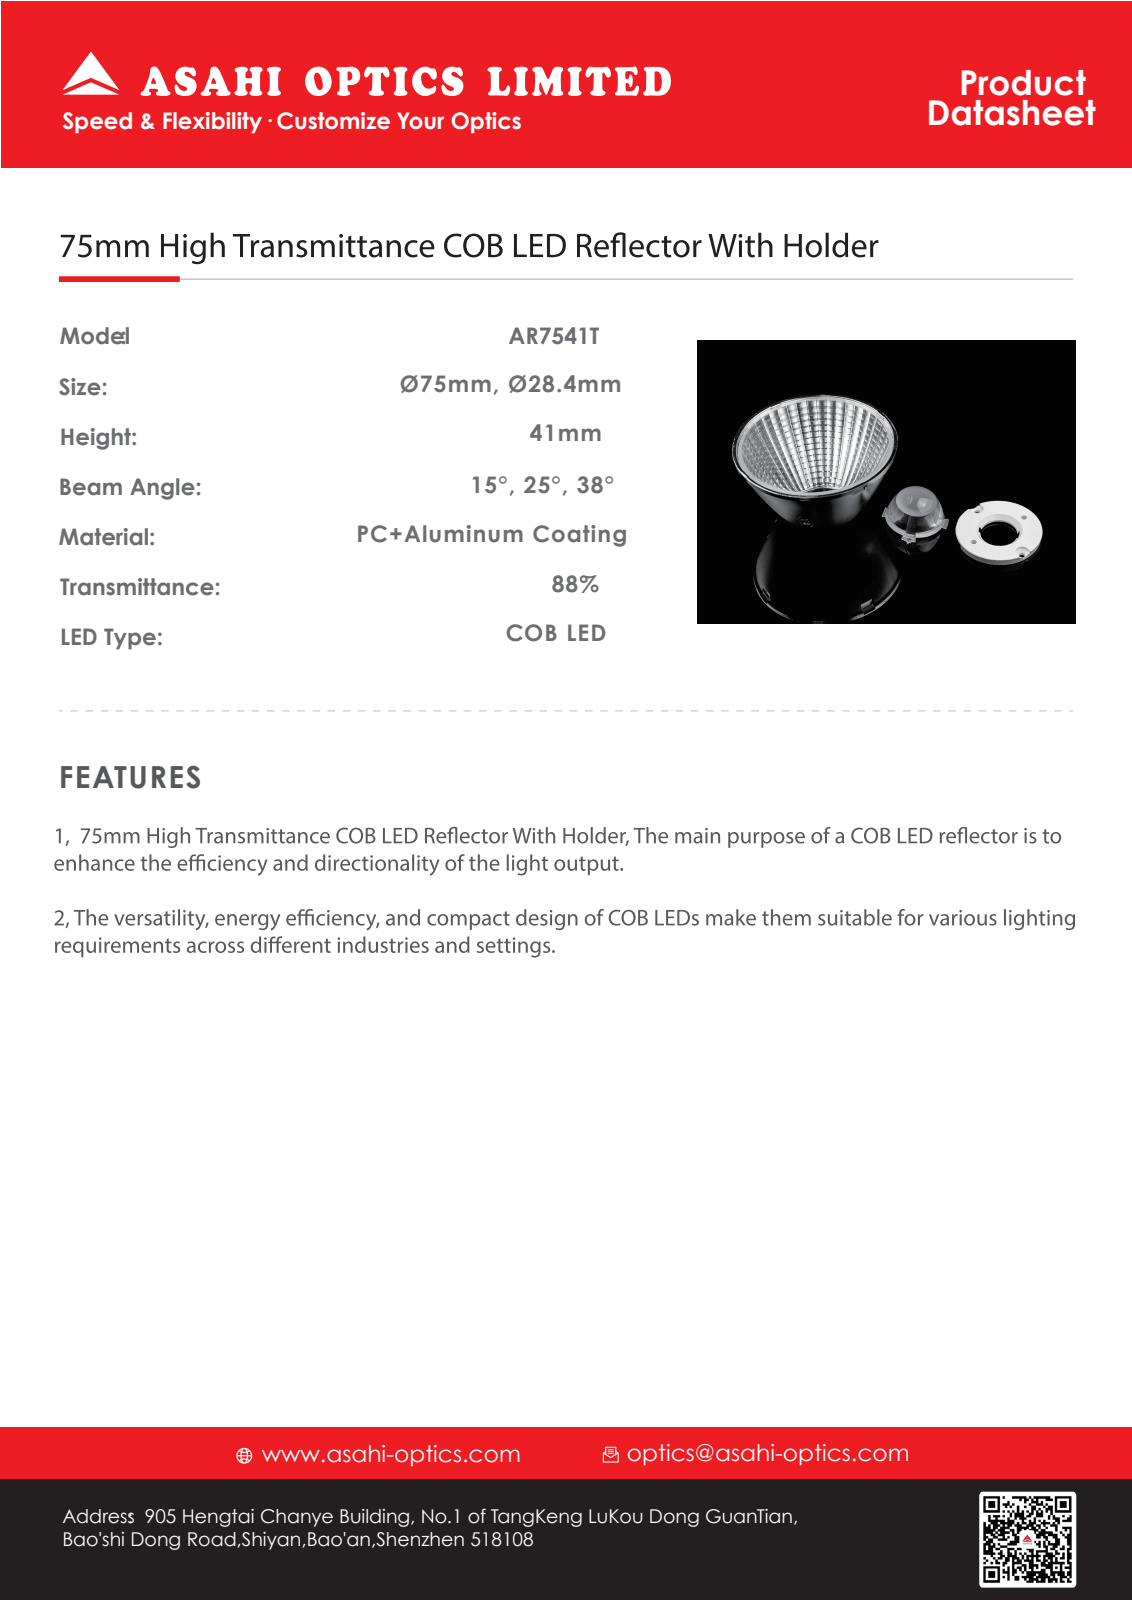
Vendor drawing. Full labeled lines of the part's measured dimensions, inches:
STEP written by: SolidWorks 2014 (CONFIG_CONTROL_DESIGN)
Units: inches
Bodies: 2 solids, 359 faces (233 planar, 73 cylindrical, 53 other)
Overall size (bounding box): 2.953 × 2.953 × 1.707
Volume: 0.728 in³ · Surface area: 30.04 in²
Round holes (diameter × count): ⌀1.118 ×1, ⌀2.831 ×1
Round bosses / shafts (diameter × count): ⌀0.056 ×2, ⌀2.953 ×1, ⌀1.29 ×1
Partial cylindrical surfaces — rounded edges, fillets, slot ends (radius × count): R0.008 ×38, R0.379 ×1, R0.63 ×1, R1.398 ×1
Main face-to-face distances: 0.026, 1.589, 1.614, 0.357, 0.331, 1.257, 0.106, 1.508, 1.482, 1.151
